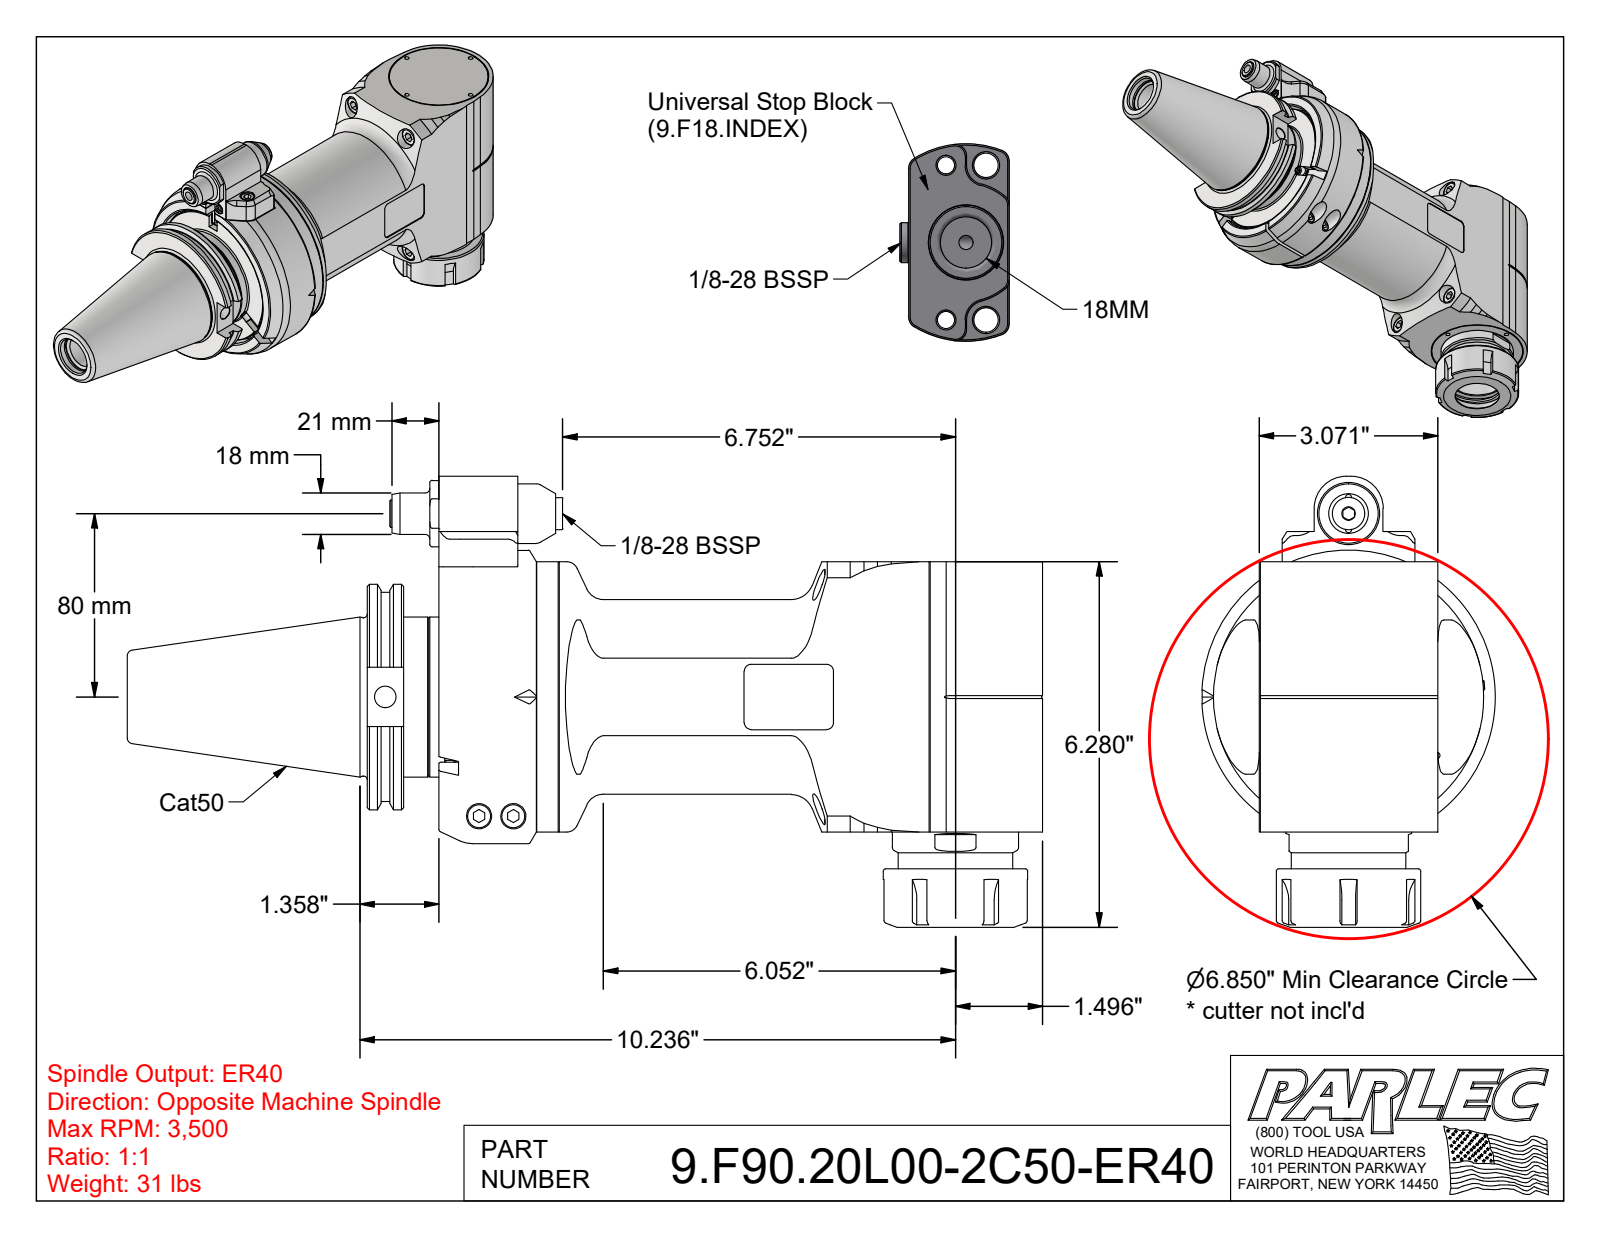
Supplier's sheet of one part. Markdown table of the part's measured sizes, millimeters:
| quantity | value |
| --- | --- |
| part name | 9.F90.20L00-2C50-ER40; 9_GA2_458_2 (Type 2, Cat50, 80mm); F9020L0-000EG0 - ER40 |
| STEP written by | Autodesk Inventor 2022 (AUTOMOTIVE_DESIGN) |
| units | millimeters |
| bodies | 5 solids, 619 faces (290 planar, 146 cylindrical, 183 other) |
| overall size | 399.6 × 196.7 × 128 |
| volume | 2 594 000 mm³ |
| surface area | 246 300 mm² |
| round holes (diameter × count) | 3.2 × 8, 5 × 4, 13.5 × 4, 2.6 × 2, 4.2 × 2, 5.3 × 2, 8 × 2, 10.4 × 2, 11 × 2, 2.5 × 1, 3 × 1, 6.5 × 1 |
| round bosses / shafts (diameter × count) | 13 × 4, 10 × 4, 6 × 4, 18 × 2, 2.5 × 2, 128 × 1, 118 × 1, 111 × 1 |
| partial cylindrical surfaces (radius × count) | 2 × 8, 15 × 6, 3 × 4, 4 × 4, 0.4 × 2, 0.5 × 2, 1 × 2, 3.5 × 2 |
| main face-to-face distances | 34, 78, 35, 1, 0.5, 40, 6, 118, 2.3, 115.7 |
| hole center spacings | 30.9, 31.5, 34, 44.6, 48.1, 49.5, 56, 78.2 |
